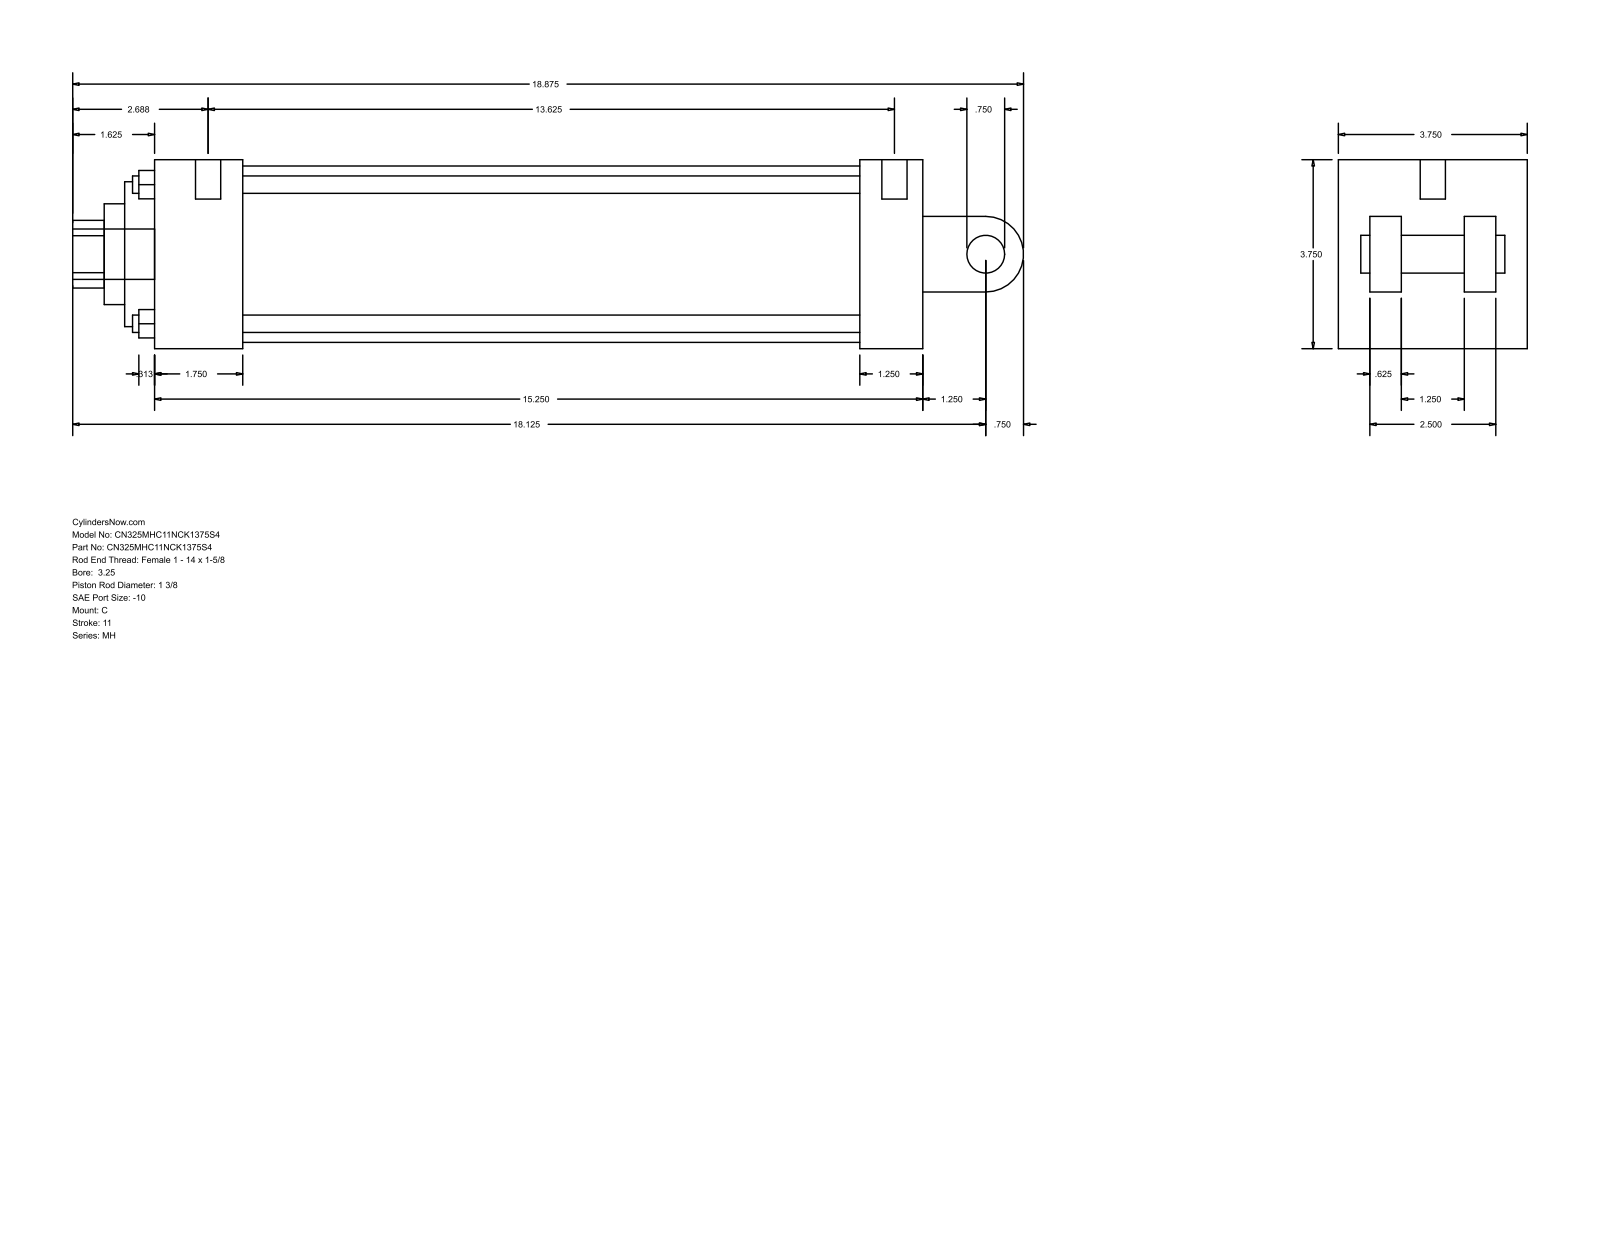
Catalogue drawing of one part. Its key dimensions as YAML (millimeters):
part_name: "MH_C__0325_1.375"
step_written_by: "GSSL Pune (CONFIG_CONTROL_DESIGN)"
units: millimeters
bodies: {solids: 0, faces: 101, planar: 71, cylindrical: 30, other: 0}
overall_size: [479.43, 95.25, 95.25]
round_holes:
  - {diameter: 8.76, count: 4}
  - {diameter: 5.56, count: 2}
  - {diameter: 12.7, count: 1}
  - {diameter: 34.92, count: 1}
  - {diameter: 50.8, count: 1}
  - {diameter: 73.03, count: 1}
  - {diameter: 88.9, count: 1}
round_bosses_or_shafts:
  - {diameter: 5.56, count: 2}
  - {diameter: 25.4, count: 1}
  - {diameter: 19.05, count: 1}
  - {diameter: 12.7, count: 1}
partial_cylinders:
  - {radius: 17.06, count: 1}
  - {radius: 19.05, count: 1}
face_to_face_distances: [95.24, 15.87, 31.74, 387.35, 63.5, 79.37, 47.63, 44.45, 355.61, 311.16]
hole_center_spacings: [49.57, 70.1, 99.14, 4.76]
